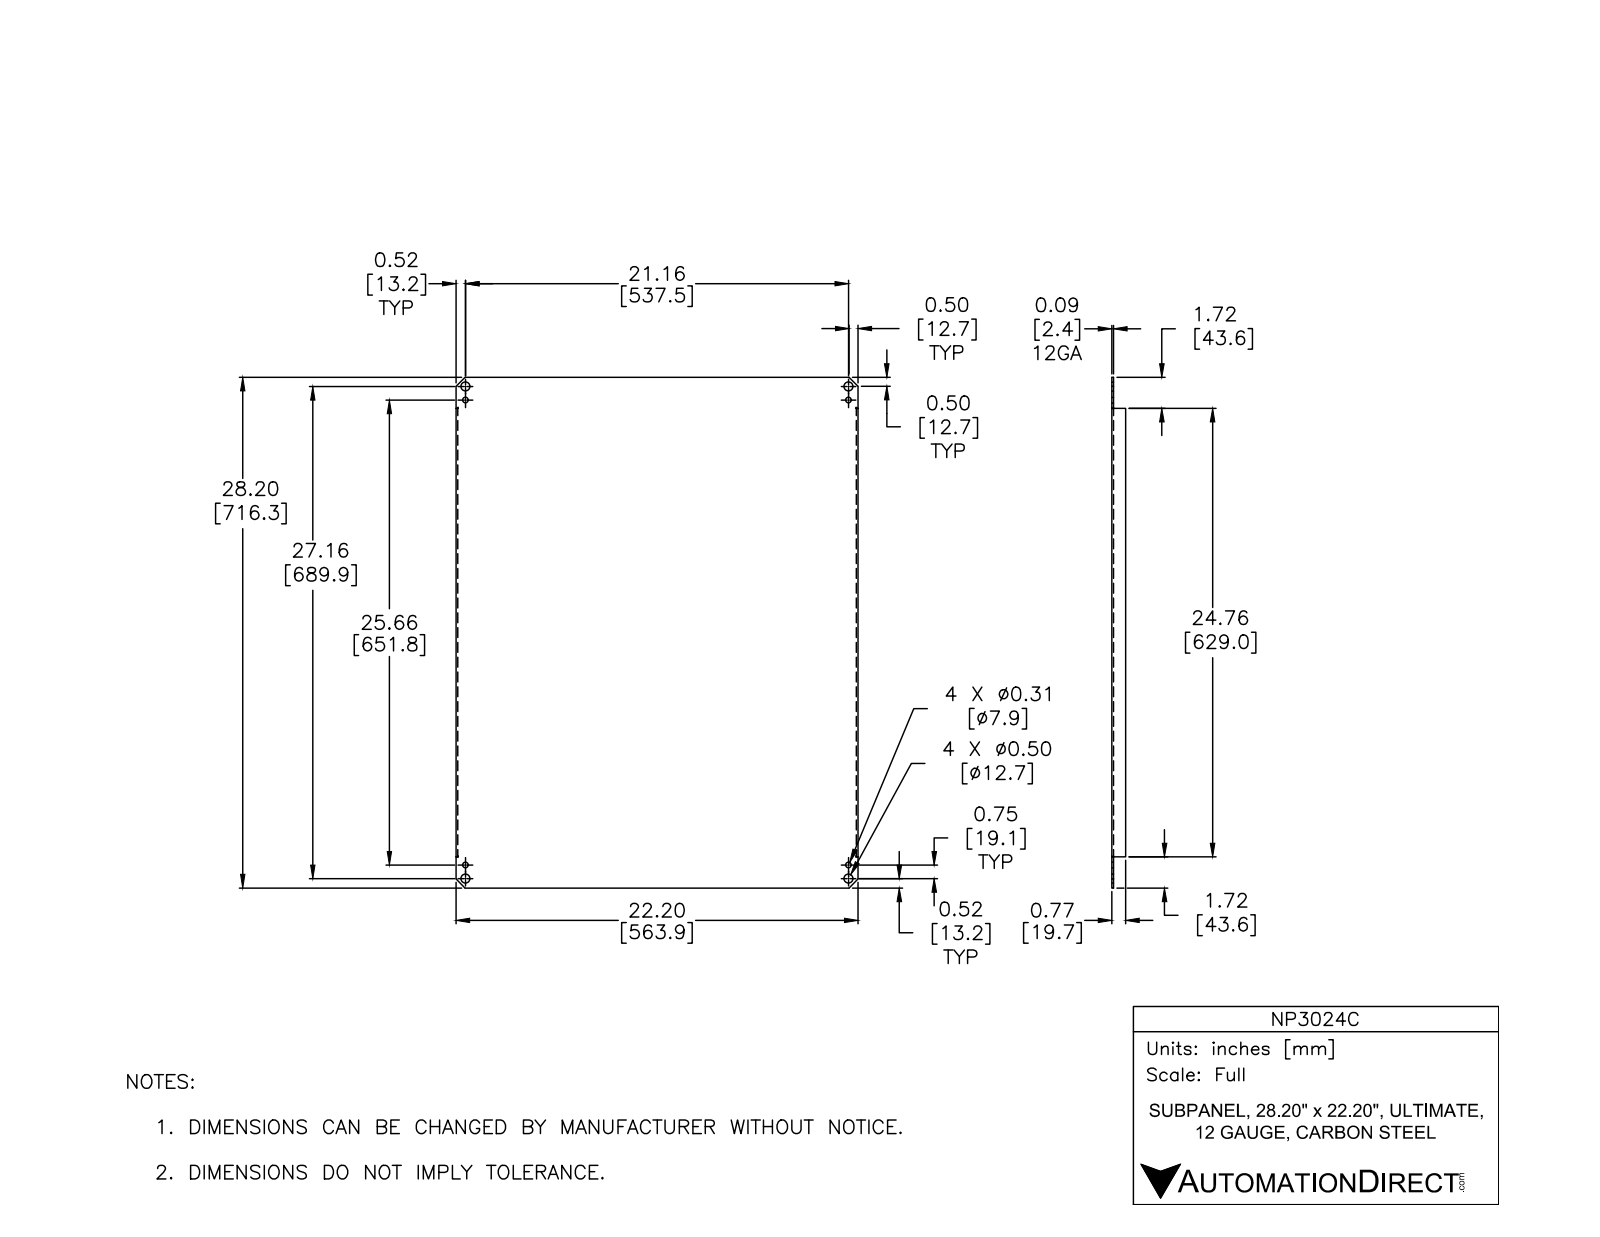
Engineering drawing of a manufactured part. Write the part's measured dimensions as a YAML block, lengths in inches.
part_name: "NP3024C"
step_written_by: "Autodesk Inventor 2012 (AUTOMOTIVE_DESIGN)"
units: inches
bodies: {solids: 1, faces: 42, planar: 30, cylindrical: 12, other: 0}
overall_size: [28.2, 22.2, 0.774]
volume: 61.58
surface_area: 1324
round_holes:
  - {diameter: 0.313, count: 4}
  - {diameter: 0.5, count: 4}
partial_cylinders:
  - {radius: 0.016, count: 2}
  - {radius: 0.109, count: 2}
face_to_face_distances: [0.094, 22.106, 22.2, 22.013, 0.68, 0.774, 28.2, 1.718, 26.482, 24.764]
hole_center_spacings: [0.75, 21.16, 21.173, 26.41, 33.841, 25.66, 27.16, 33.259]
